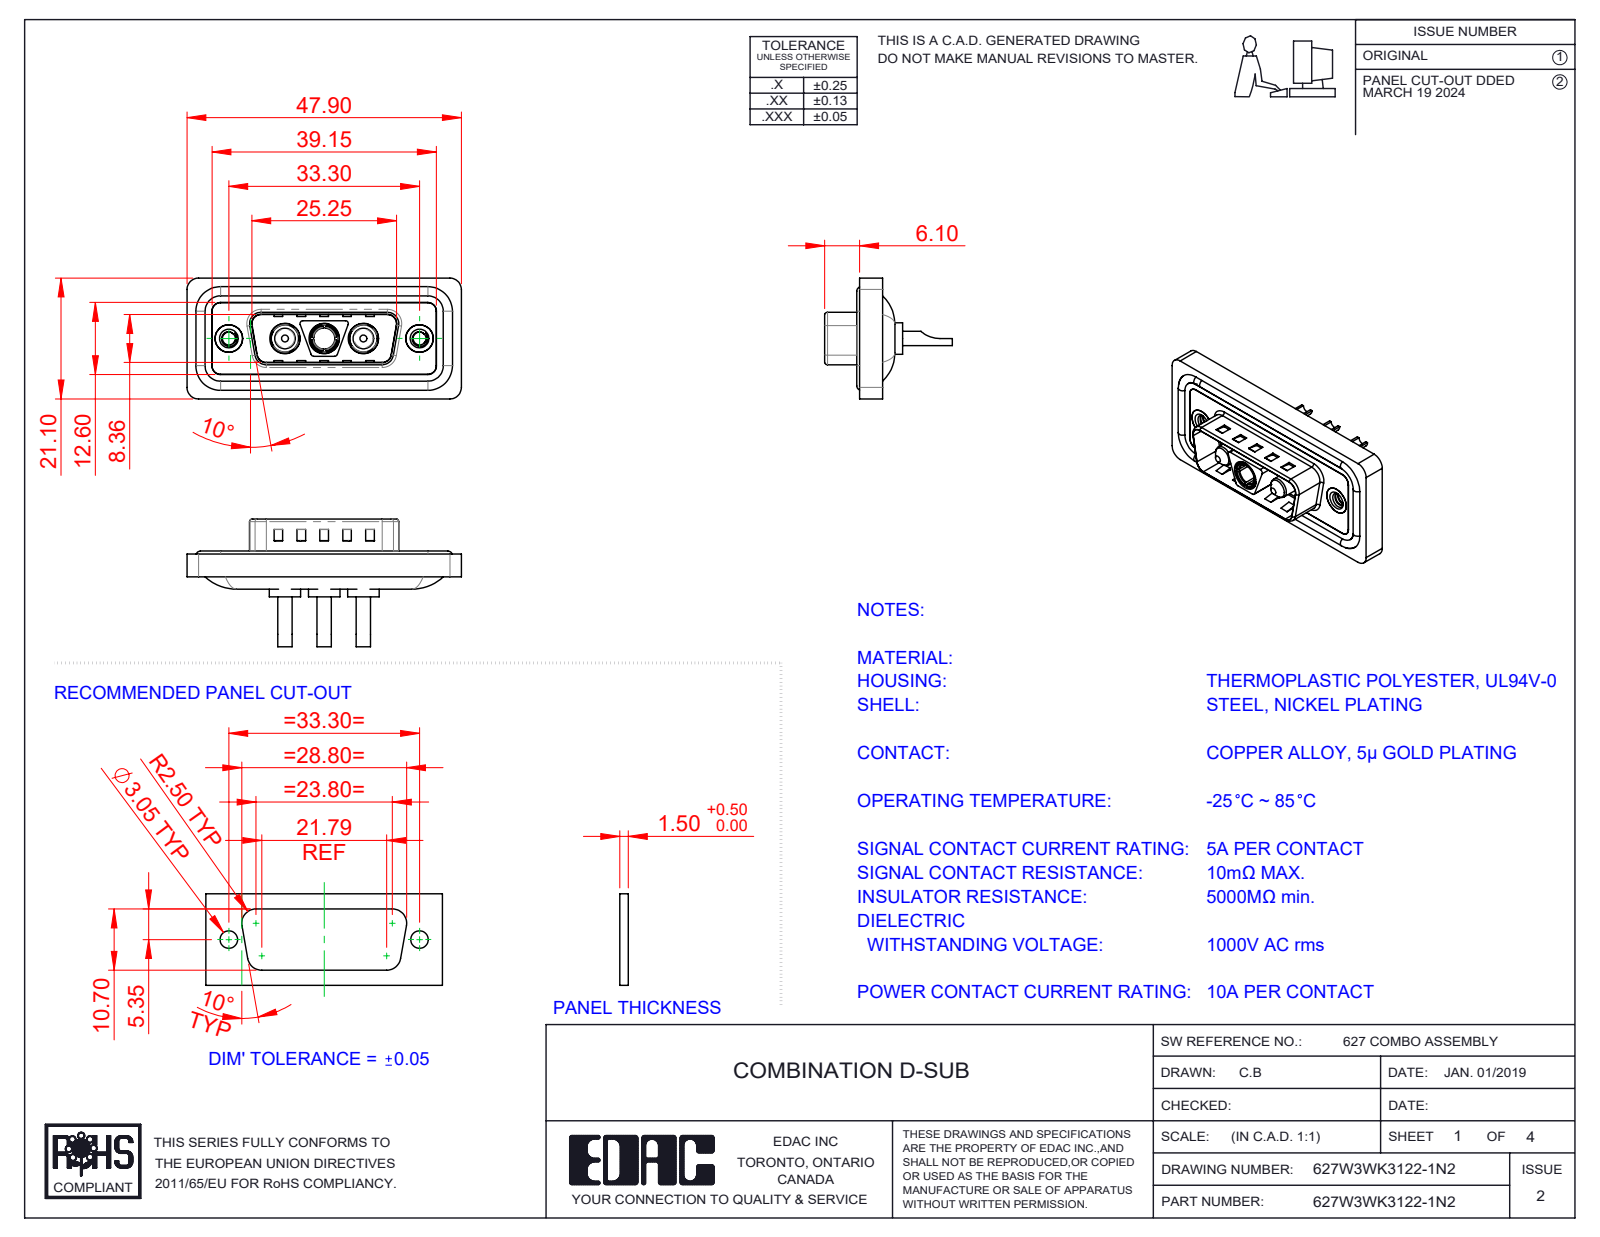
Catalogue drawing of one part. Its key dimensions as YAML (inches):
part_name: "Power Pin_10A SC; 627Combo Waterproof Housing_15 Contacts; 627Combo Housing_3WK3; 627Combo Shell Front_15 Contacts (+4 more)"
step_written_by: "SolidWorks 2023 (CONFIG_CONTROL_DESIGN)"
units: inches
bodies: {solids: 13, faces: 625, planar: 237, cylindrical: 259, other: 129}
overall_size: [1.886, 0.878, 0.831]
volume: 0.347
surface_area: 14.37
round_holes:
  - {diameter: 0.067, count: 3}
  - {diameter: 0.191, count: 3}
  - {diameter: 0.209, count: 3}
  - {diameter: 0.089, count: 2}
  - {diameter: 0.157, count: 2}
  - {diameter: 0.189, count: 2}
  - {diameter: 0.197, count: 2}
  - {diameter: 0.146, count: 1}
round_bosses_or_shafts:
  - {diameter: 0.063, count: 4}
  - {diameter: 0.217, count: 3}
  - {diameter: 0.205, count: 3}
  - {diameter: 0.187, count: 3}
  - {diameter: 0.148, count: 3}
  - {diameter: 0.098, count: 3}
  - {diameter: 0.193, count: 2}
  - {diameter: 0.142, count: 2}
partial_cylinders:
  - {radius: 0.059, count: 26}
  - {radius: 0.079, count: 20}
  - {radius: 0.02, count: 12}
  - {radius: 0.063, count: 8}
  - {radius: 0.01, count: 4}
  - {radius: 0.024, count: 4}
  - {radius: 0.026, count: 4}
  - {radius: 0.035, count: 4}
face_to_face_distances: [0.016, 0.043, 0.059, 0.02, 0.063, 0.122, 0.114, 0.157, 0.032, 0.377]
hole_center_spacings: [0.27, 0.386, 0.656, 0.925, 0.539, 1.311]
